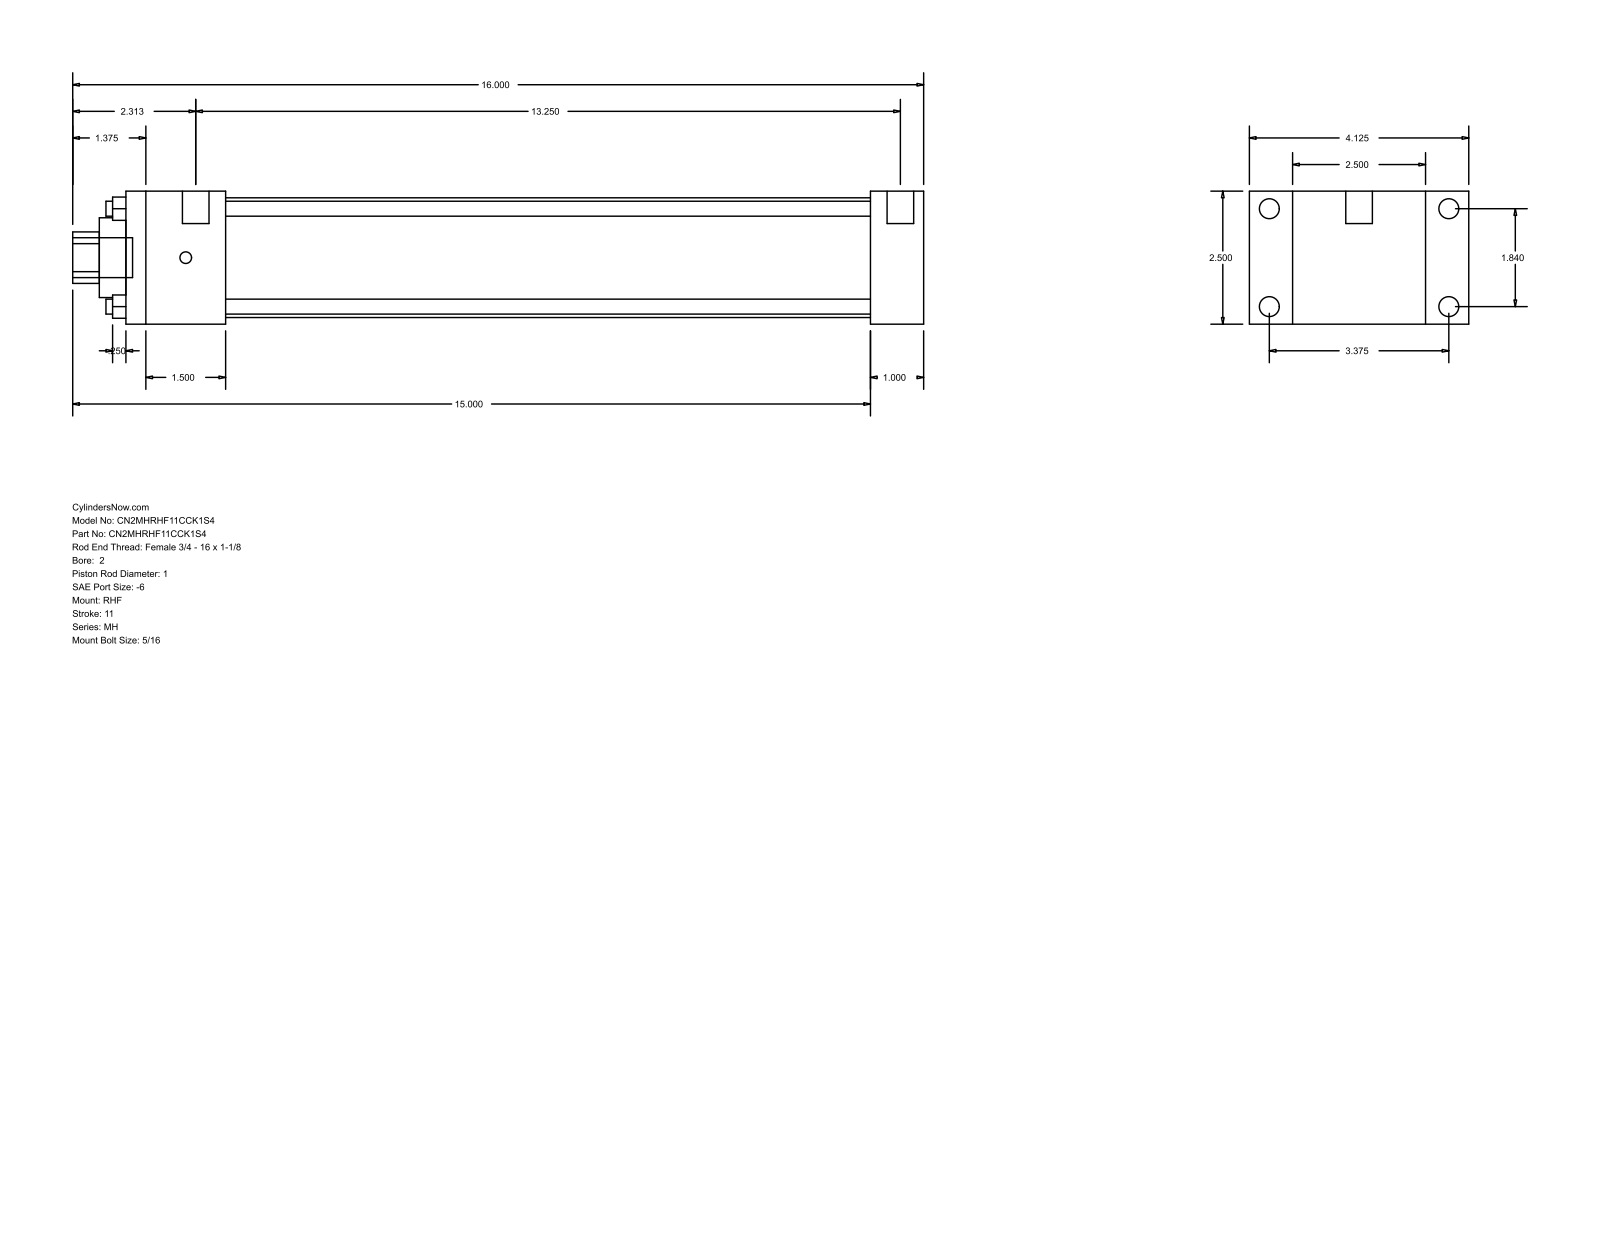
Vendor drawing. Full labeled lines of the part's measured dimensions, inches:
Part name (STEP PRODUCT): MH_RHF__0200_1
STEP written by: GSSL Pune (CONFIG_CONTROL_DESIGN)
Units: inches
Bodies: 0 solids, 88 faces (60 planar, 28 cylindrical, 0 other)
Overall size (bounding box): 16 × 4.125 × 2.5
Round holes (diameter × count): ⌀0.281 ×4, ⌀1 ×1, ⌀1.5 ×1, ⌀2.25 ×1
Round bosses / shafts (diameter × count): ⌀0.375 ×4, ⌀0.219 ×4, ⌀0.5 ×2, ⌀0.75 ×1
Partial cylindrical surfaces — rounded edges, fillets, slot ends (radius × count): R0.484 ×1
Main face-to-face distances: 2.5, 1, 0.813, 3.313, 15, 14, 4.125, 1.875, 12.125, 13.125
Hole centre spacings: 1.301, 1.84, 2.602
